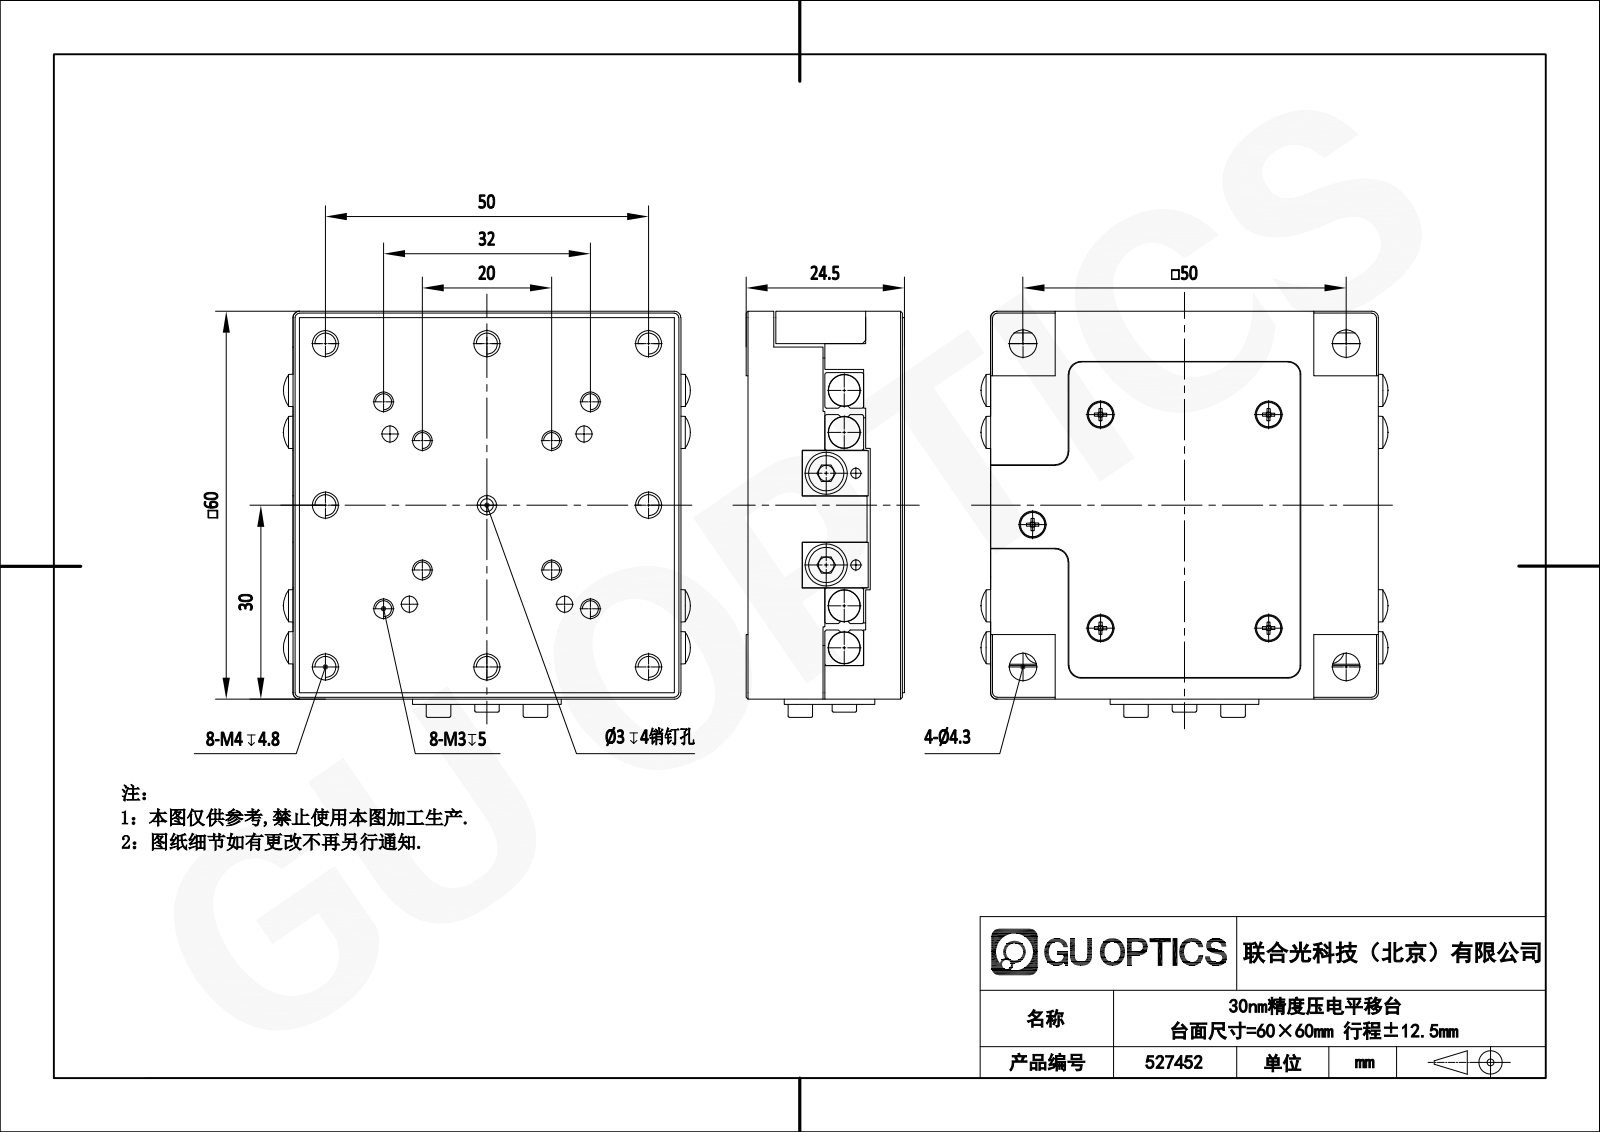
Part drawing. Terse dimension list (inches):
name: VR2-60x11Z.STEP; R.STEP; LS2-0618-41zz____.STEP; 527452-527472.STEP (+8 more)
written by: SolidWorks 2020 (CONFIG_CONTROL_DESIGN)
unit: in
bodies: 24 solids, 1220 faces (577 planar, 375 cylindrical, 268 other)
size: 2.481 × 2.472 × 0.965
volume: 5.057 in³; area: 66.99 in²
holes: 39× ⌀0.098, 18× ⌀0.063, 16× ⌀0.177, 9× ⌀0.087, 8× ⌀0.13, 5× ⌀0.126, 5× ⌀0.165, 4× ⌀0.169, 4× ⌀0.315, 3× ⌀0.138, 3× ⌀0.236, 2× ⌀0.256
bosses: 8× ⌀0.15, 8× ⌀0.079, 5× ⌀0.217, 5× ⌀0.118
rounds: 19× R0.079, 17× R0.059, 14× R0.039, 6× R0.031, 4× R0.012, 4× R0.075, 4× R0.118, 3× R0.157
face distances: 0.248, 0.236, 0.953, 0.128, 0.705, 0.577, 0.825, 0.256, 0.02, 2.362
hole spacings: 0.591, 1.181, 0.404, 1.311, 1.344, 0.276, 0.296, 0.651
